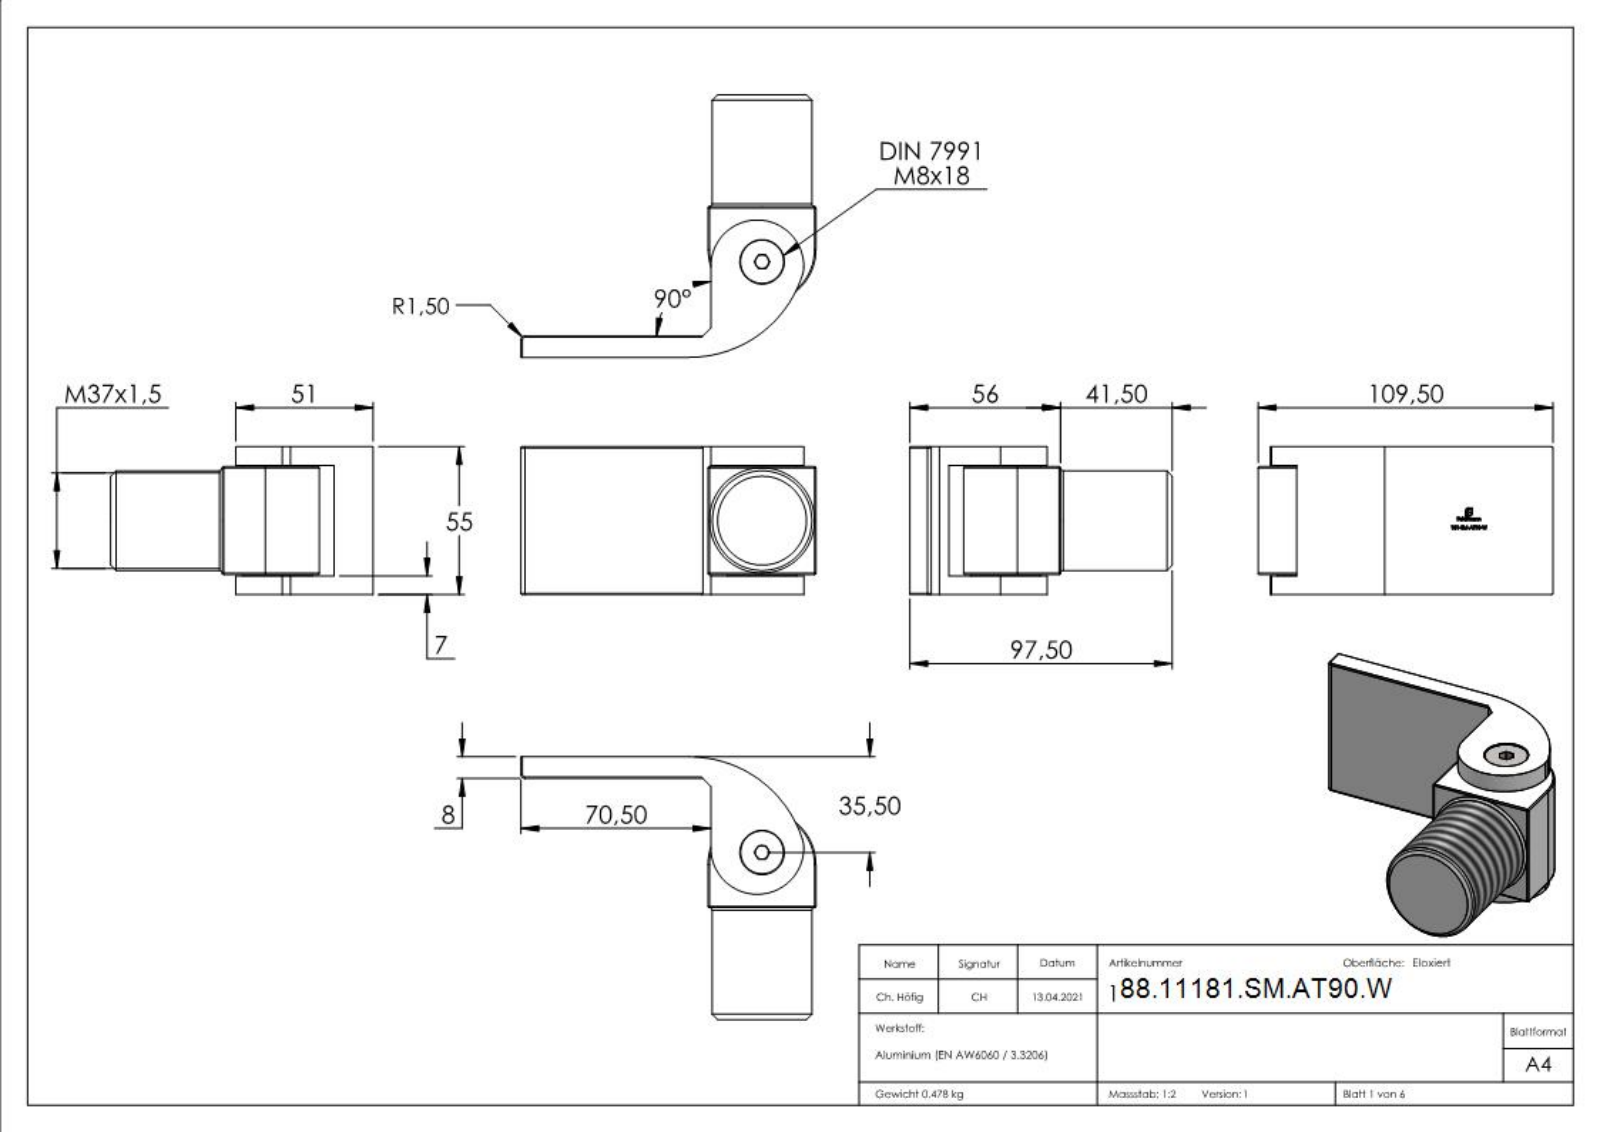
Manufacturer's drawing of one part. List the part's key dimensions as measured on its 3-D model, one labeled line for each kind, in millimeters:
Part name (STEP PRODUCT): 181-SM-AT90-W; Teil1; DIN-7991 M3-M10; Teil3 (+7 more)
STEP written by: SolidWorks 2018 (CONFIG_CONTROL_DESIGN)
Units: millimetres
Bodies: 11 solids, 549 faces (245 planar, 78 cylindrical, 226 other)
Overall size (bounding box): 14000.35 × 5999.86 × 5999.7
Volume: 152 361 mm³ · Surface area: 43 747 mm²
Round holes (diameter × count): ⌀6.8 ×1, ⌀8.5 ×1, ⌀16.5 ×1, ⌀19 ×1, ⌀23.6 ×1, ⌀26 ×1
Round bosses / shafts (diameter × count): ⌀37 ×1, ⌀23.4 ×1, ⌀18.8 ×1, ⌀16 ×1, ⌀8 ×1
Partial cylindrical surfaces — rounded edges, fillets, slot ends (radius × count): R0.5 ×12, R1.5 ×1, R10 ×1, R17.25 ×1, R20 ×1, R44.11 ×1
Main face-to-face distances: 8, 48, 7, 6.5, 41.5, 55, 0.5, 7.5, 47.5, 40.5
